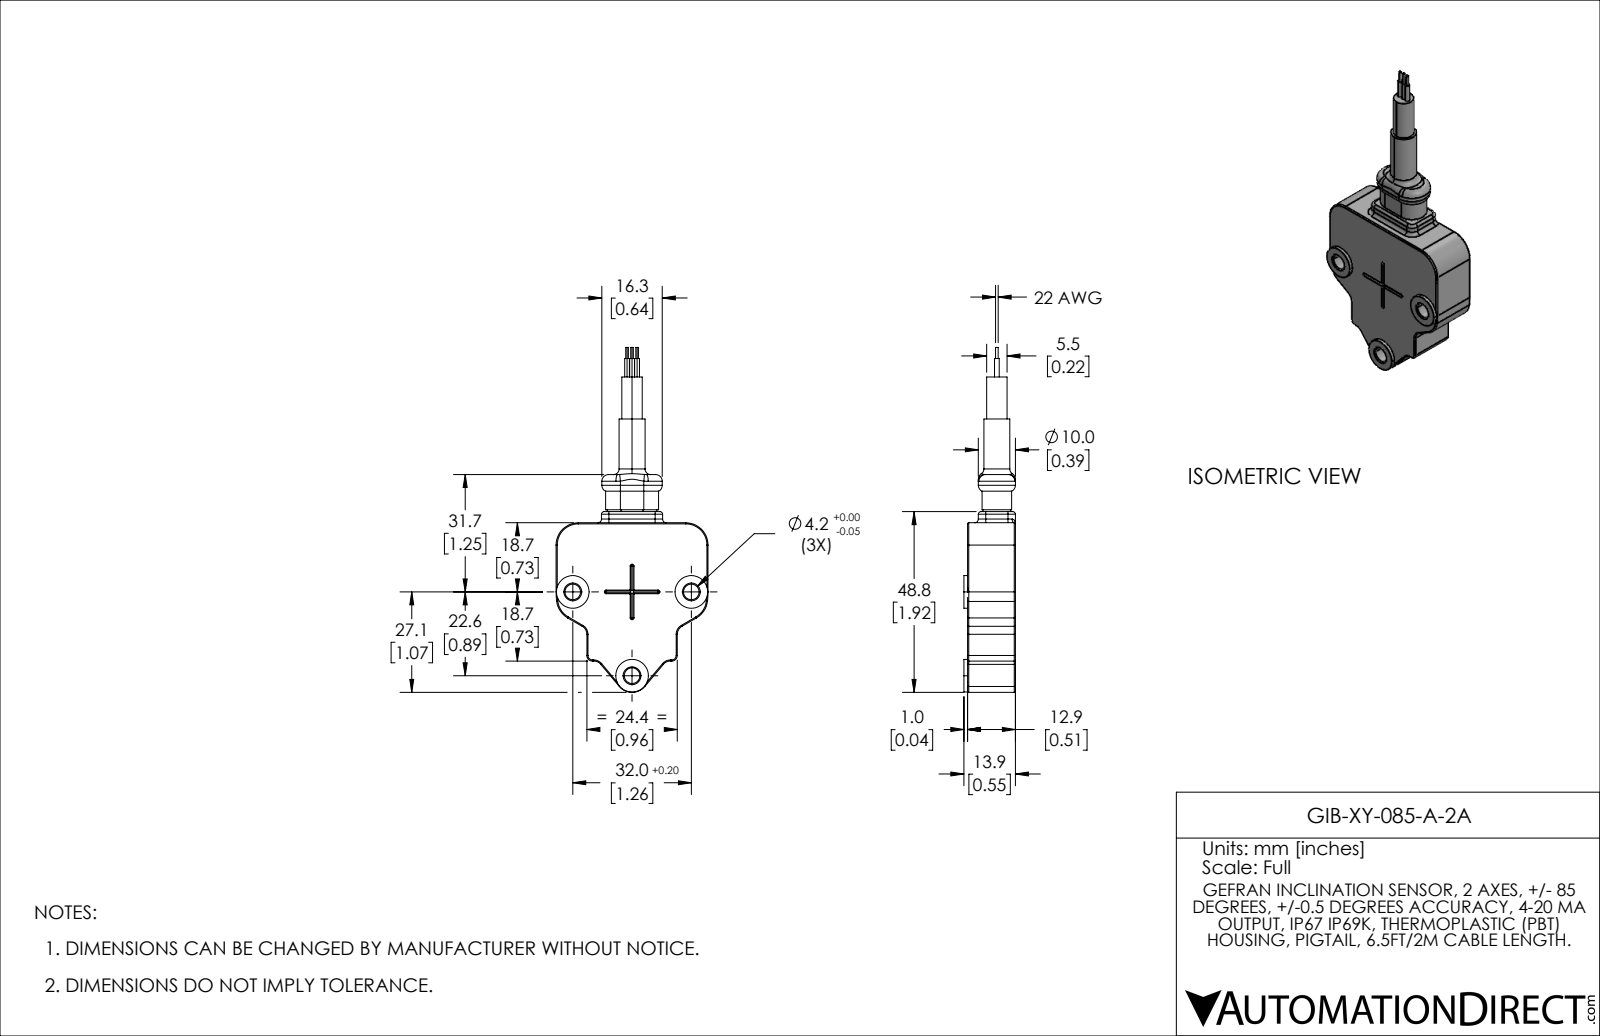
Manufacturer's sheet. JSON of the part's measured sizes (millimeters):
{"part_name": "GIB-XY-085-A-2A", "step_written_by": "SolidWorks 2021 (AUTOMOTIVE_DESIGN)", "units": "millimeters", "bodies": {"solids": 1, "faces": 201, "planar": 47, "cylindrical": 87, "other": 67}, "overall_size": [93, 41, 13.9], "volume_mm3": 20420, "surface_area_mm2": 6435, "round_holes": [[4.2, 3]], "round_bosses_or_shafts": [[8.8, 3], [1.3, 3], [0.7, 3], [7, 1], [5.5, 1]], "partial_cylinders_radius": [[0.3, 20], [0.2, 4], [0.7, 4], [2, 4], [2.5, 4], [6, 4], [1, 3], [1.5, 2]], "face_to_face_distances": [12.9, 1, 41, 8.3, 32.7, 13.9, 24.4, 9, 3.9, 3], "hole_center_spacings": [27.7, 32]}
